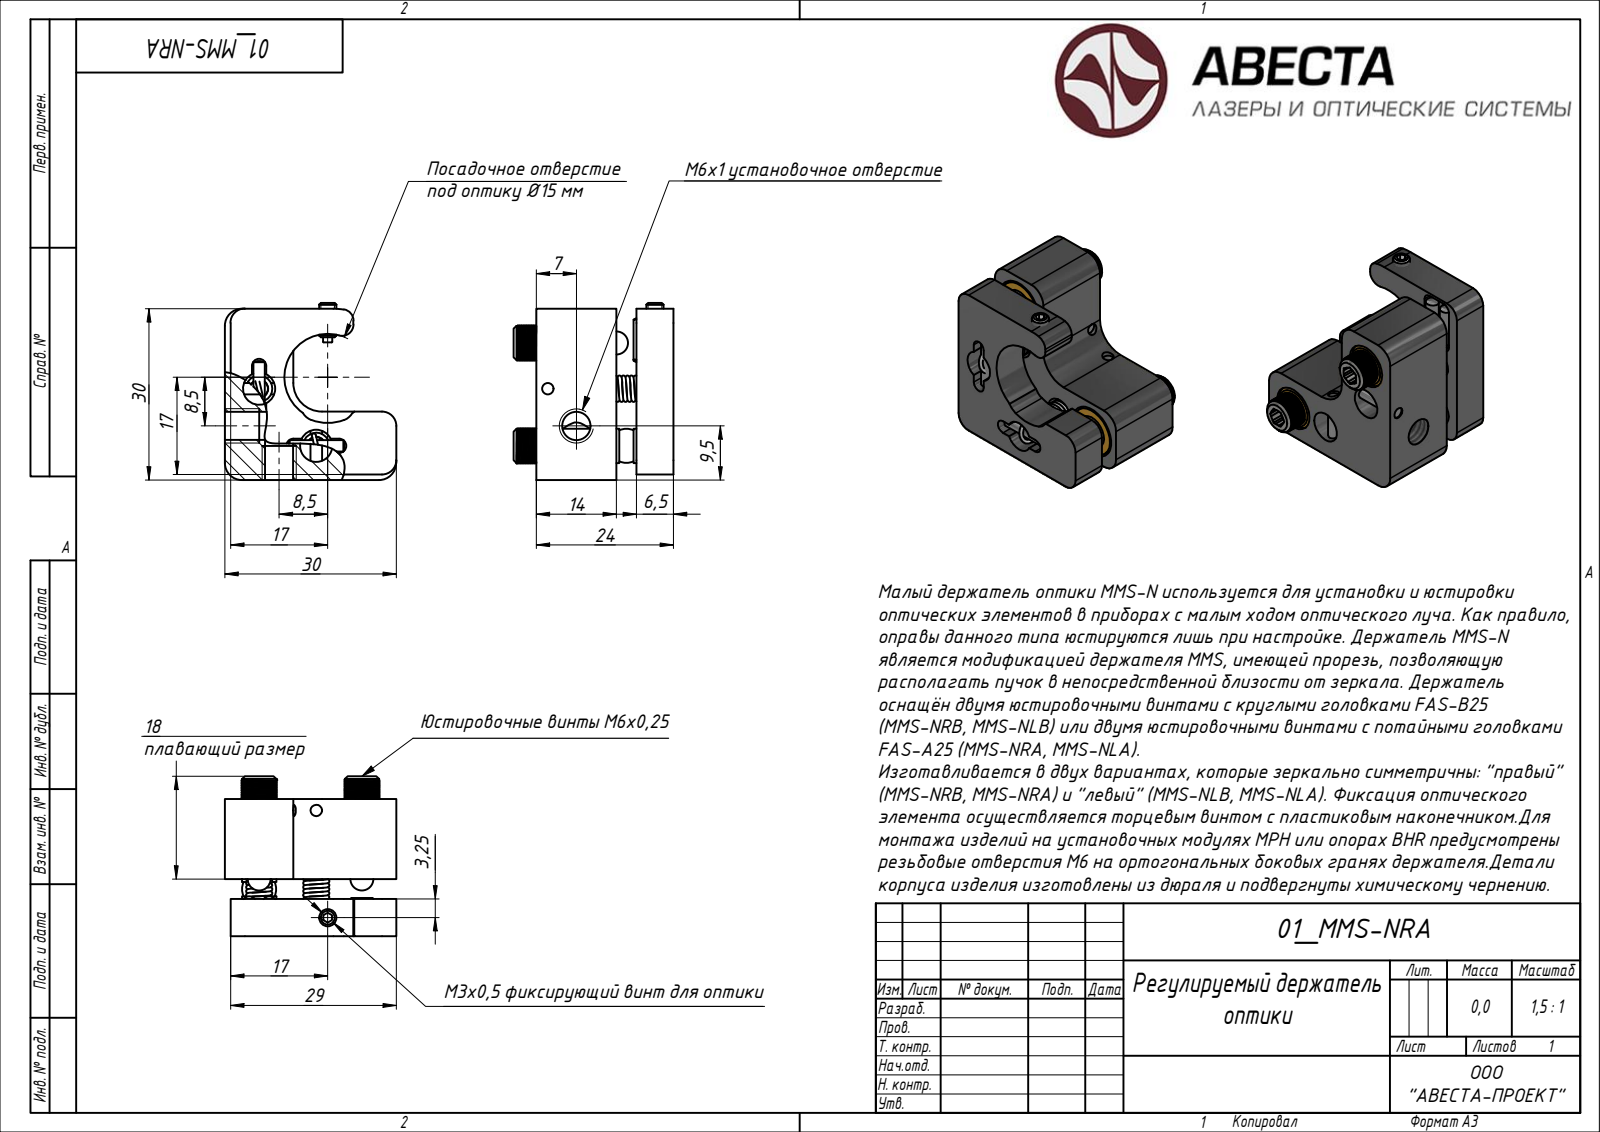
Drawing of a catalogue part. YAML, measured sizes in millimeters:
step_written_by: "ST-DEVELOPER v15 (AUTOMOTIVE_DESIGN)"
units: millimeters
bodies: {solids: 19, faces: 309, planar: 108, cylindrical: 0, other: 201}
overall_size: [31, 30, 26.7]
volume: 10446
surface_area: 9511
face_to_face_distances: [6.5, 3.5, 24, 10, 12, 14, 1, 17.5, 11, 18]
